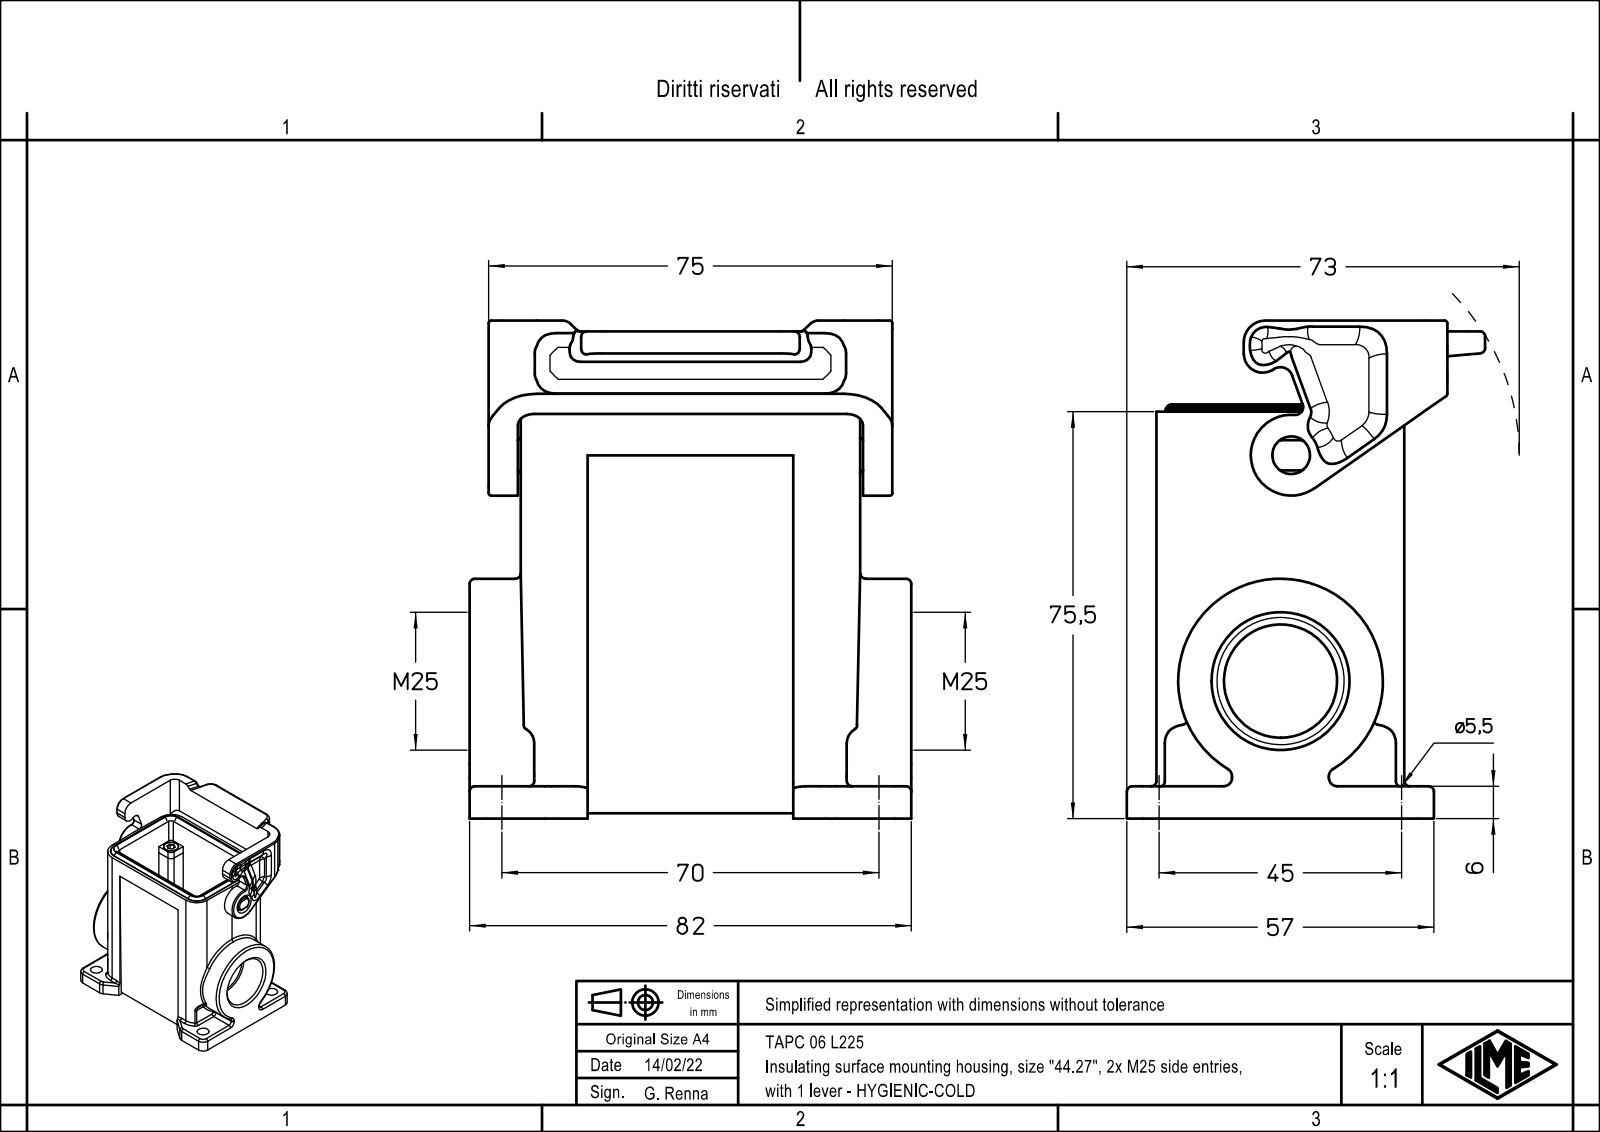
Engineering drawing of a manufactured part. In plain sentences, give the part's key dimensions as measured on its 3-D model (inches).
The part is named "TAPH 06 L225". Its 3-D file was written by "Creo Elements/Direct Modeling 20.1B 02-Apr-2019 (C) Parametric Technology GmbH (AUTOMOTIVE_DESIGN)". It is 1 solid with 325 faces: 161 planar, 128 cylindrical and 36 other. Overall it measures 3.638 by 3.228 by 2.618 inches. Its volume is 8.389 cubic inches and its surface area 72.84 square inches. Round holes: 4 of diameter 0.217, 1 of diameter 0.827, 1 of diameter 0.929. Round bosses or shafts: 1 of diameter 1.496. Partial cylindrical surfaces (rounded edges, fillets, slot ends): 17 of radius 0.118, 10 of radius 0.079, 9 of radius 0.059, 8 of radius 0.039, 8 of radius 0.051, 4 of radius 0.02, 4 of radius 0.236, 4 of radius 0.276. The main face-to-face distances are 1.811, 0.213, 1.598, 1.598, 1.385, 0.213, 0.217, 0.587, 0.039, 2.642. The hole center spacings are 1.772, 2.756, 3.276.
